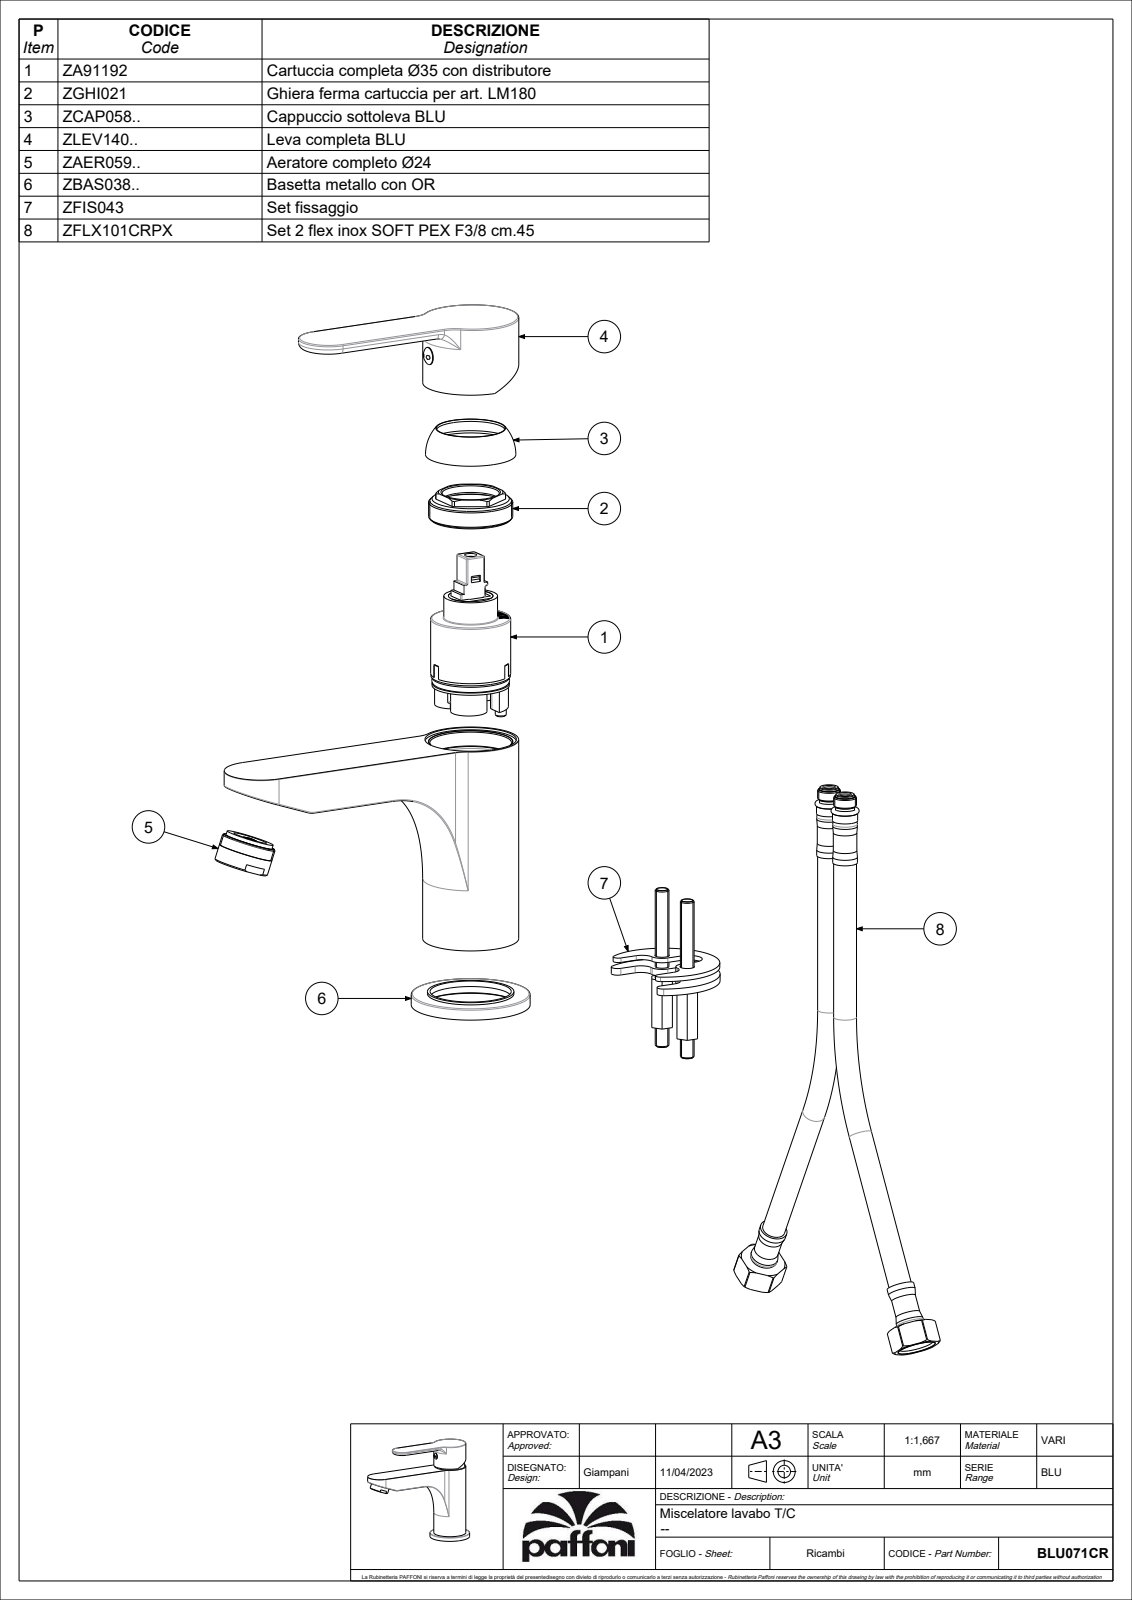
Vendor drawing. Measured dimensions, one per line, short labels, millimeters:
name: BLU071CR
written by: CREO PARAMETRIC BY PTC INC, 2020044 (CONFIG_CONTROL_DESIGN)
unit: mm
bodies: 3 solids, 2660 faces (1911 planar, 465 cylindrical, 284 other)
size: 148 × 127.7 × 52
volume: 124 579 mm³; area: 93 180 mm²
holes: 4× ⌀5, 3× ⌀9, 3× ⌀12, 2× ⌀3.3, 2× ⌀6, 2× ⌀6.5, 2× ⌀8, 1× ⌀3, 1× ⌀3.5, 1× ⌀4, 1× ⌀4.6, 1× ⌀16
bosses: 2× ⌀14, 2× ⌀12, 2× ⌀11, 2× ⌀10.5, 2× ⌀10, 2× ⌀6, 2× ⌀4.8, 1× ⌀52
rounds: 70× R0.5, 23× R1, 20× R0.3, 16× R1.5, 14× R0.54, 14× R3, 9× R1.2, 5× R10
face distances: 3, 29, 32, 2.7, 1, 18, 26, 5, 95.2, 21
hole spacings: 13.6, 0.71, 2.83, 8.51, 8.6, 9.66, 9.85, 11.18
